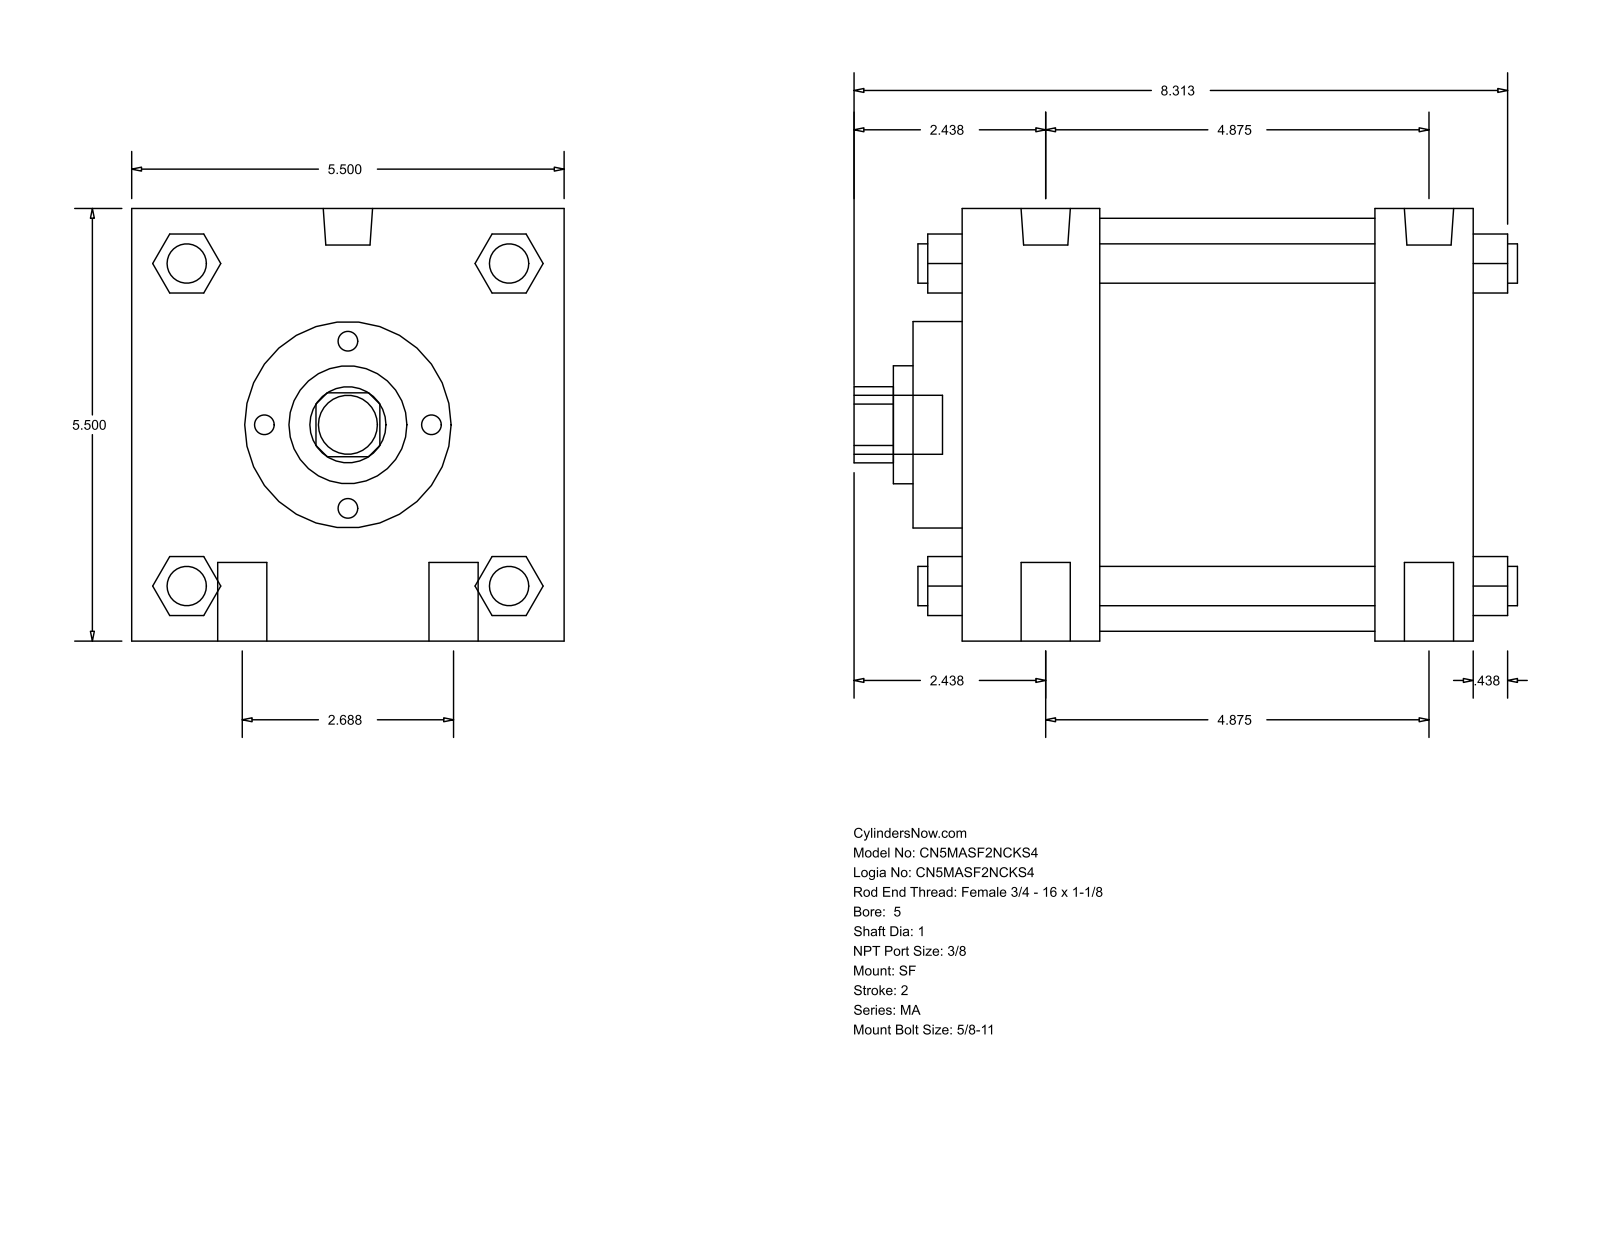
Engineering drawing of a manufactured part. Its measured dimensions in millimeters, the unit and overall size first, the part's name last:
Units: millimetres
Overall size (bounding box): 214.31 × 139.7 × 139.7
Round holes (diameter × count): ⌀25.4 ×1, ⌀38.1 ×1, ⌀66.67 ×1, ⌀133.35 ×1
Round bosses / shafts (diameter × count): ⌀15.88 ×4, ⌀12.7 ×4, ⌀15.93 ×2, ⌀11.11 ×2, ⌀19.05 ×1
Partial cylindrical surfaces — rounded edges, fillets, slot ends (radius × count): R12.29 ×1
Main face-to-face distances: 139.7, 165.11, 44.46, 133.36, 88.9, 120.65, 31.75, 15.87, 60.33, 149.23
Bodies: 0 solids, 126 faces (95 planar, 31 cylindrical, 0 other)
Part name (STEP PRODUCT): MA_SF__0500_1
STEP written by: GSSL Pune (CONFIG_CONTROL_DESIGN)
